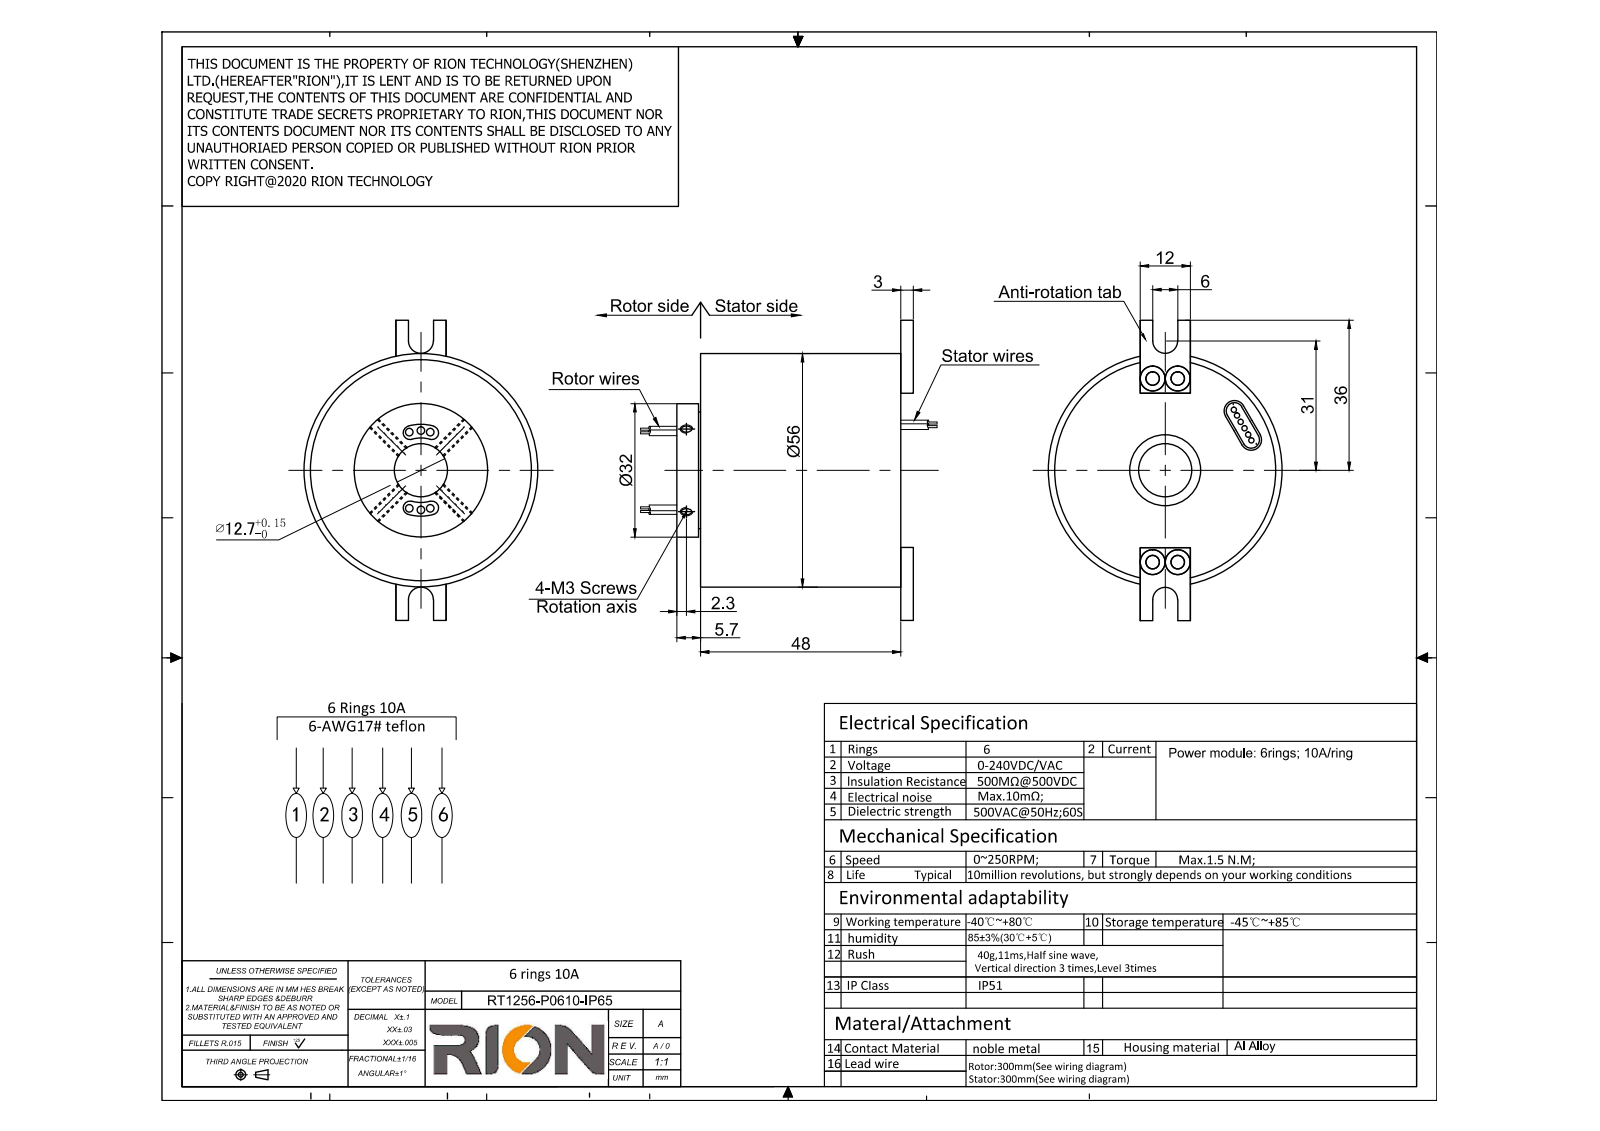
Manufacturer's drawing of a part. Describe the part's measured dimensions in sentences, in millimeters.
The part is named "RT1256-P0610-IP65". Its 3-D file was written by "SolidWorks 2014 (AUTOMOTIVE_DESIGN)". It is 1 solid with 155 faces: 56 planar, 83 cylindrical and 16 other. Overall it measures 72.2 by 72 by 56 millimeters. Its volume is 116 566 cubic millimeters and its surface area 19 897 square millimeters. Round holes: 6 of diameter 2.5, 4 of diameter 3.2, 1 of diameter 12.7, 1 of diameter 15.8, 1 of diameter 53. Round bosses or shafts: 12 of diameter 1.8, 1 of diameter 56, 1 of diameter 52.9, 1 of diameter 52.8, 1 of diameter 32, 1 of diameter 28, 1 of diameter 15.5. Partial cylindrical surfaces (rounded edges, fillets, slot ends): 4 of radius 1.62, 2 of radius 2, 2 of radius 3, 1 of radius 8.12, 1 of radius 11.38. The main face-to-face distances are 48, 5.7, 53.7, 3, 56.7, 51, 5, 0.7, 48.7, 51.7. The hole center spacings are 22.7, 6, 45, 45.4.
